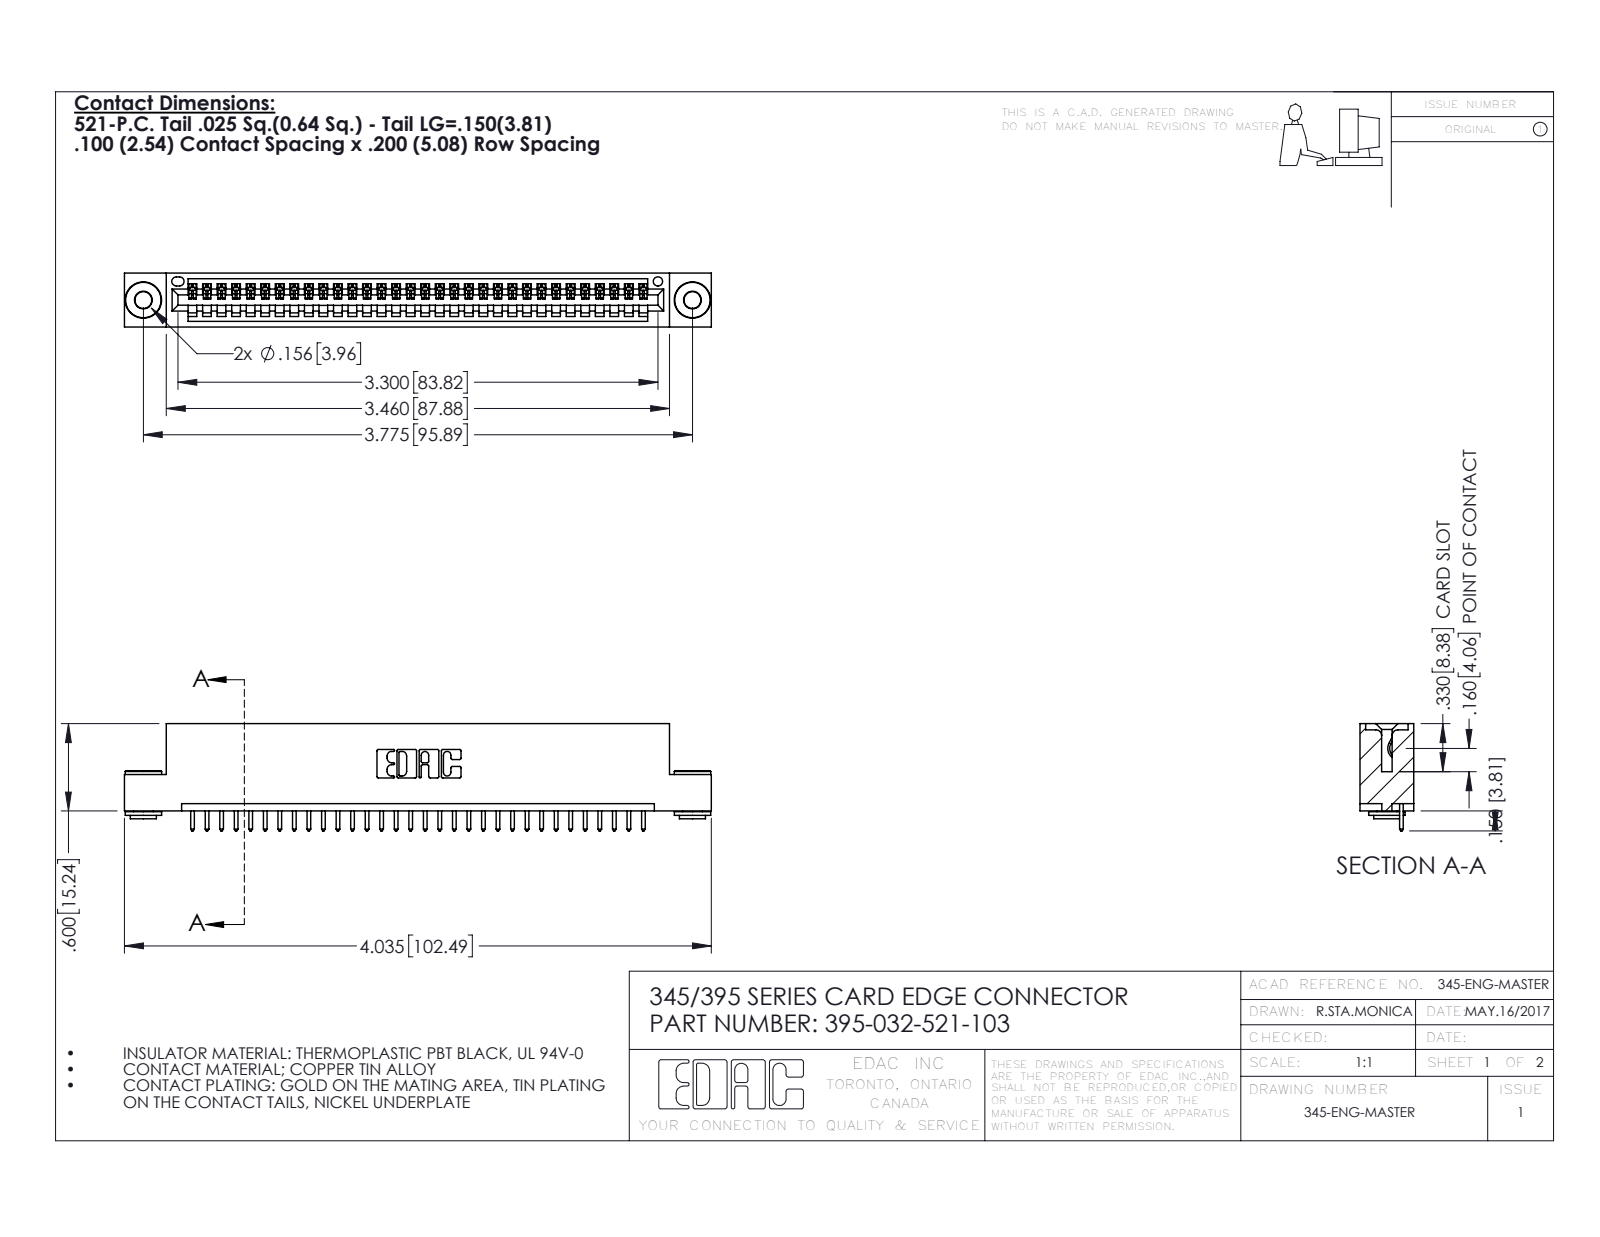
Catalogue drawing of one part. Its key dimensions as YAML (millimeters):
part_name: "345-250-002_345-250-002-102; 395-032-521-103; 345-292-001_345-293-121; 345 Part_Flush Mounting Lugs - 0.156 Dia-TH"
step_written_by: "SolidWorks 2016 (CONFIG_CONTROL_DESIGN)"
units: millimeters
bodies: {solids: 35, faces: 2020, planar: 1370, cylindrical: 642, other: 8}
overall_size: [102.5, 18.7, 9.4]
volume: 9590
surface_area: 12450
round_holes:
  - {diameter: 2.9, count: 2}
  - {diameter: 4, count: 2}
  - {diameter: 1.6, count: 1}
round_bosses_or_shafts:
  - {diameter: 6.4, count: 2}
  - {diameter: 4.6, count: 2}
  - {diameter: 3.5, count: 2}
partial_cylinders:
  - {radius: 0.2, count: 64}
  - {radius: 0.3, count: 64}
  - {radius: 0.3, count: 22}
  - {radius: 0.2, count: 6}
  - {radius: 0.8, count: 6}
  - {radius: 0.7, count: 3}
  - {radius: 0.8, count: 2}
  - {radius: 1, count: 2}
face_to_face_distances: [1.8, 7.6, 5.1, 9.4, 0.6, 2.5, 6.9, 5.7, 3.8, 1.8]
hole_center_spacings: [6.9, 89.9, 95.9]
